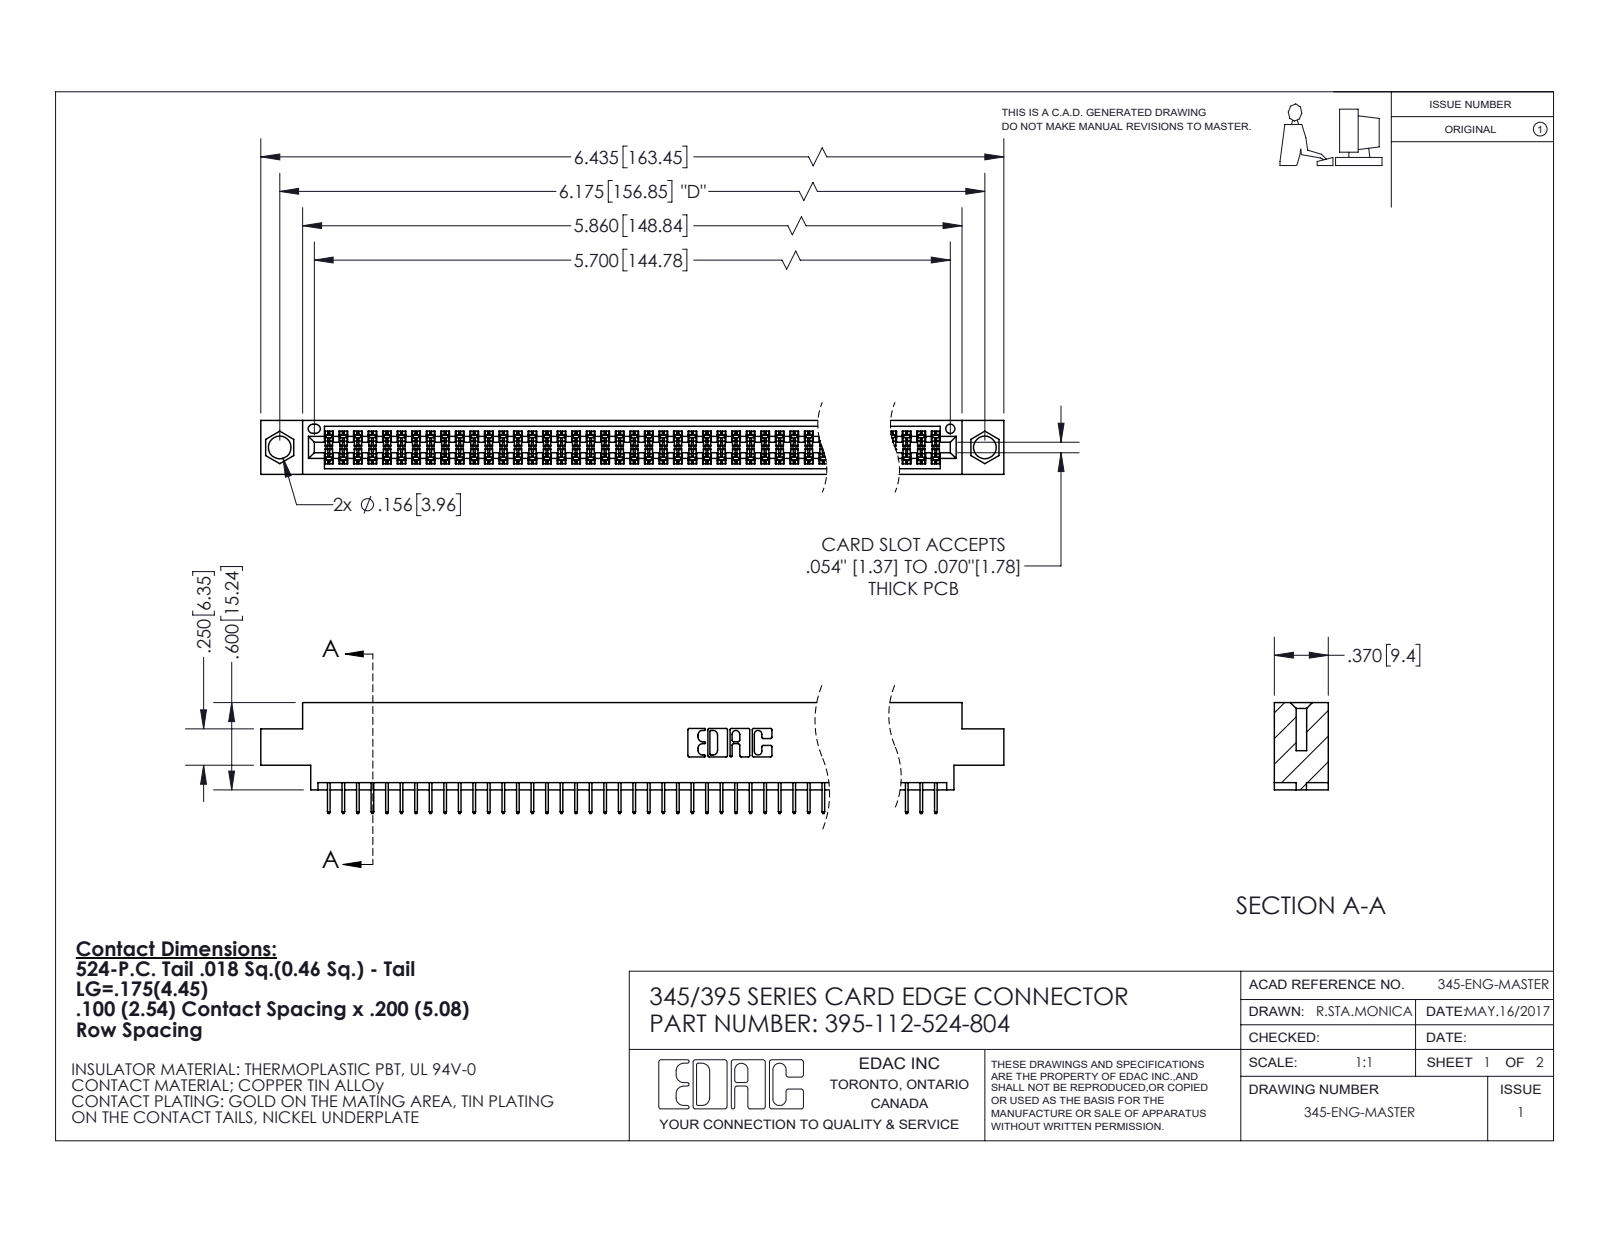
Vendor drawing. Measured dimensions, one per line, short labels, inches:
name: 345-292-001_345-293-124; 345 Part_0.170 Offset - 0.156 Dia-TI; 395-112-524-804
written by: SolidWorks 2020 (CONFIG_CONTROL_DESIGN)
unit: in
bodies: 113 solids, 6192 faces (4466 planar, 1726 cylindrical, 0 other)
size: 6.435 × 0.762 × 0.37
volume: 0.953 in³; area: 35.5 in²
holes: 2× ⌀0.156, 1× ⌀0.064
rounds: 224× R0.006, 22× R0.01, 6× R0.007, 6× R0.031, 3× R0.026, 2× R0.014, 2× R0.019, 2× R0.022
face distances: 0.072, 0.298, 0.37, 0.2, 0.098, 0.272, 0.025, 0.225, 0.072, 0.175
hole spacings: 0.27, 5.939, 6.175
